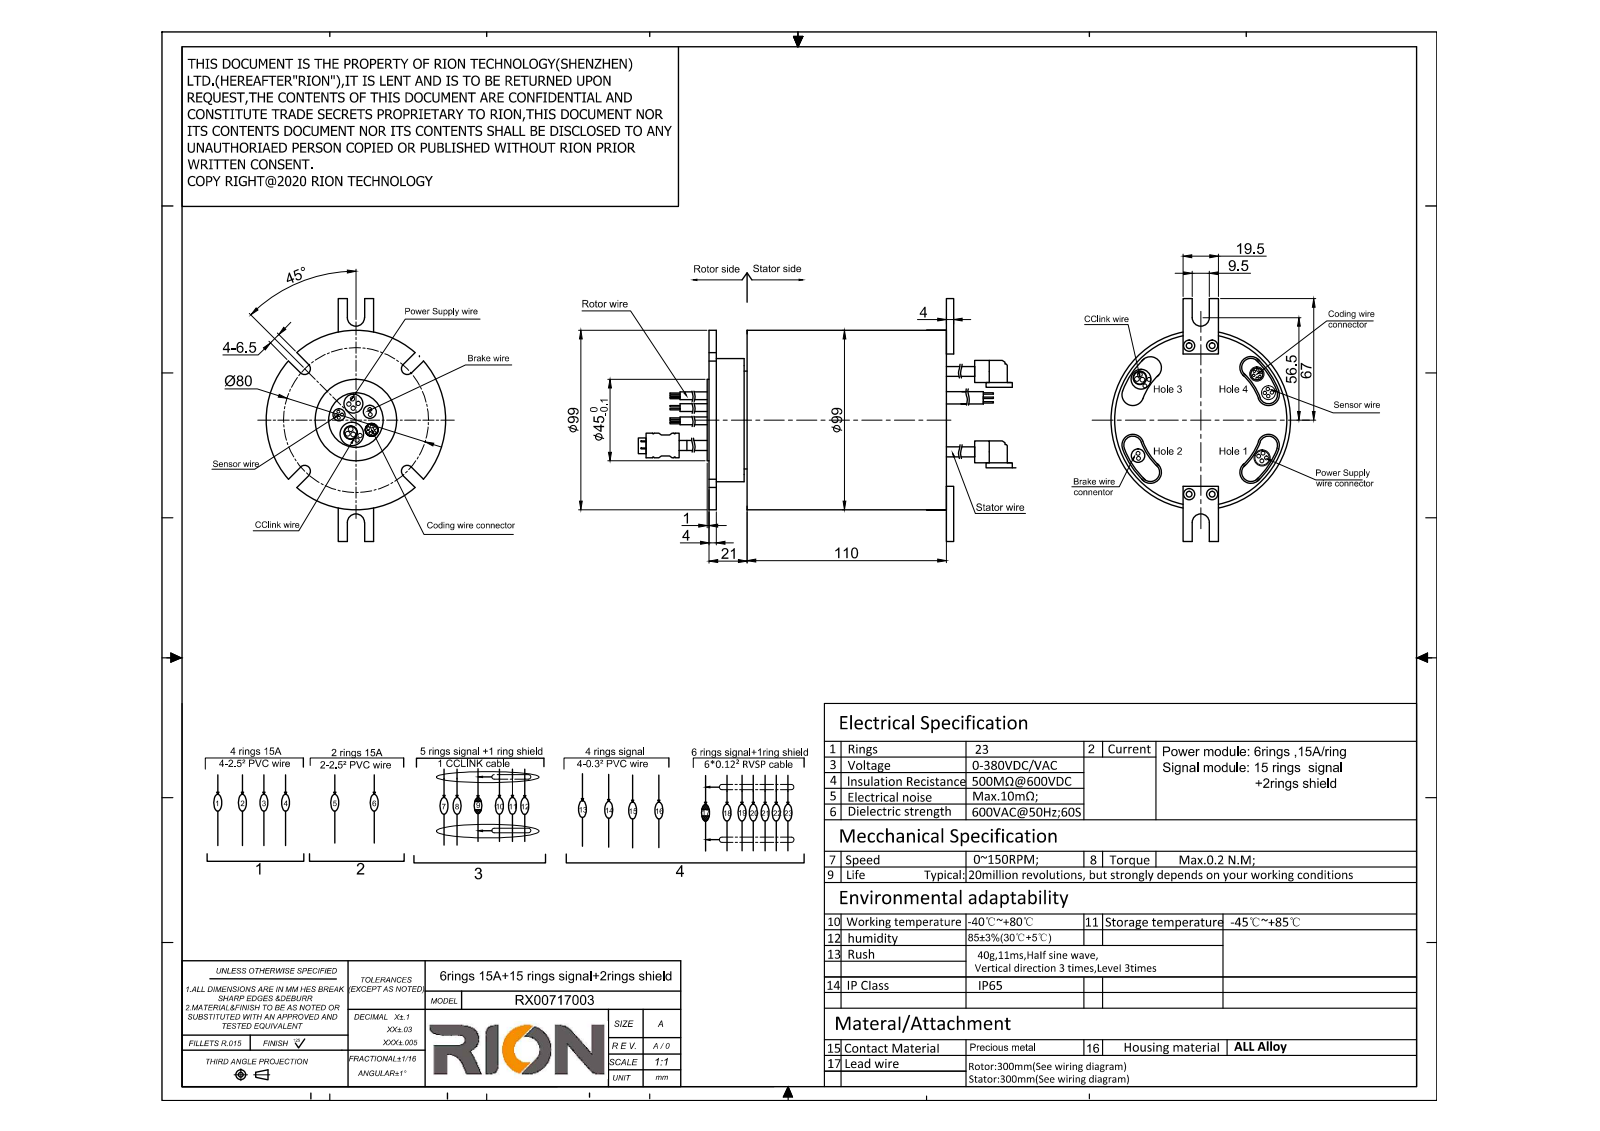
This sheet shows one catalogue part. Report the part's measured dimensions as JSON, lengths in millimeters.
{"part_name": "RZ099-P0615-S17-IP65", "step_written_by": "SolidWorks 2014 (CONFIG_CONTROL_DESIGN)", "units": "millimeters", "bodies": {"solids": 1, "faces": 143, "planar": 52, "cylindrical": 75, "other": 16}, "overall_size": [170, 134, 99], "volume_mm3": 951427, "surface_area_mm2": 73853, "round_holes": [[3.2, 4], [30, 1], [95.1, 1]], "round_bosses_or_shafts": [[99, 1], [95, 1], [68, 1], [54, 1], [45, 1], [13, 1], [11, 1], [10.46, 1]], "partial_cylinders_radius": [[6, 8], [3.25, 4], [4.75, 2], [34.01, 1], [46, 1]], "face_to_face_distances": [131, 110, 21, 4, 127, 17, 1, 5, 111.6, 1.6], "hole_center_spacings": [41.49, 12.7, 82, 82.98]}
